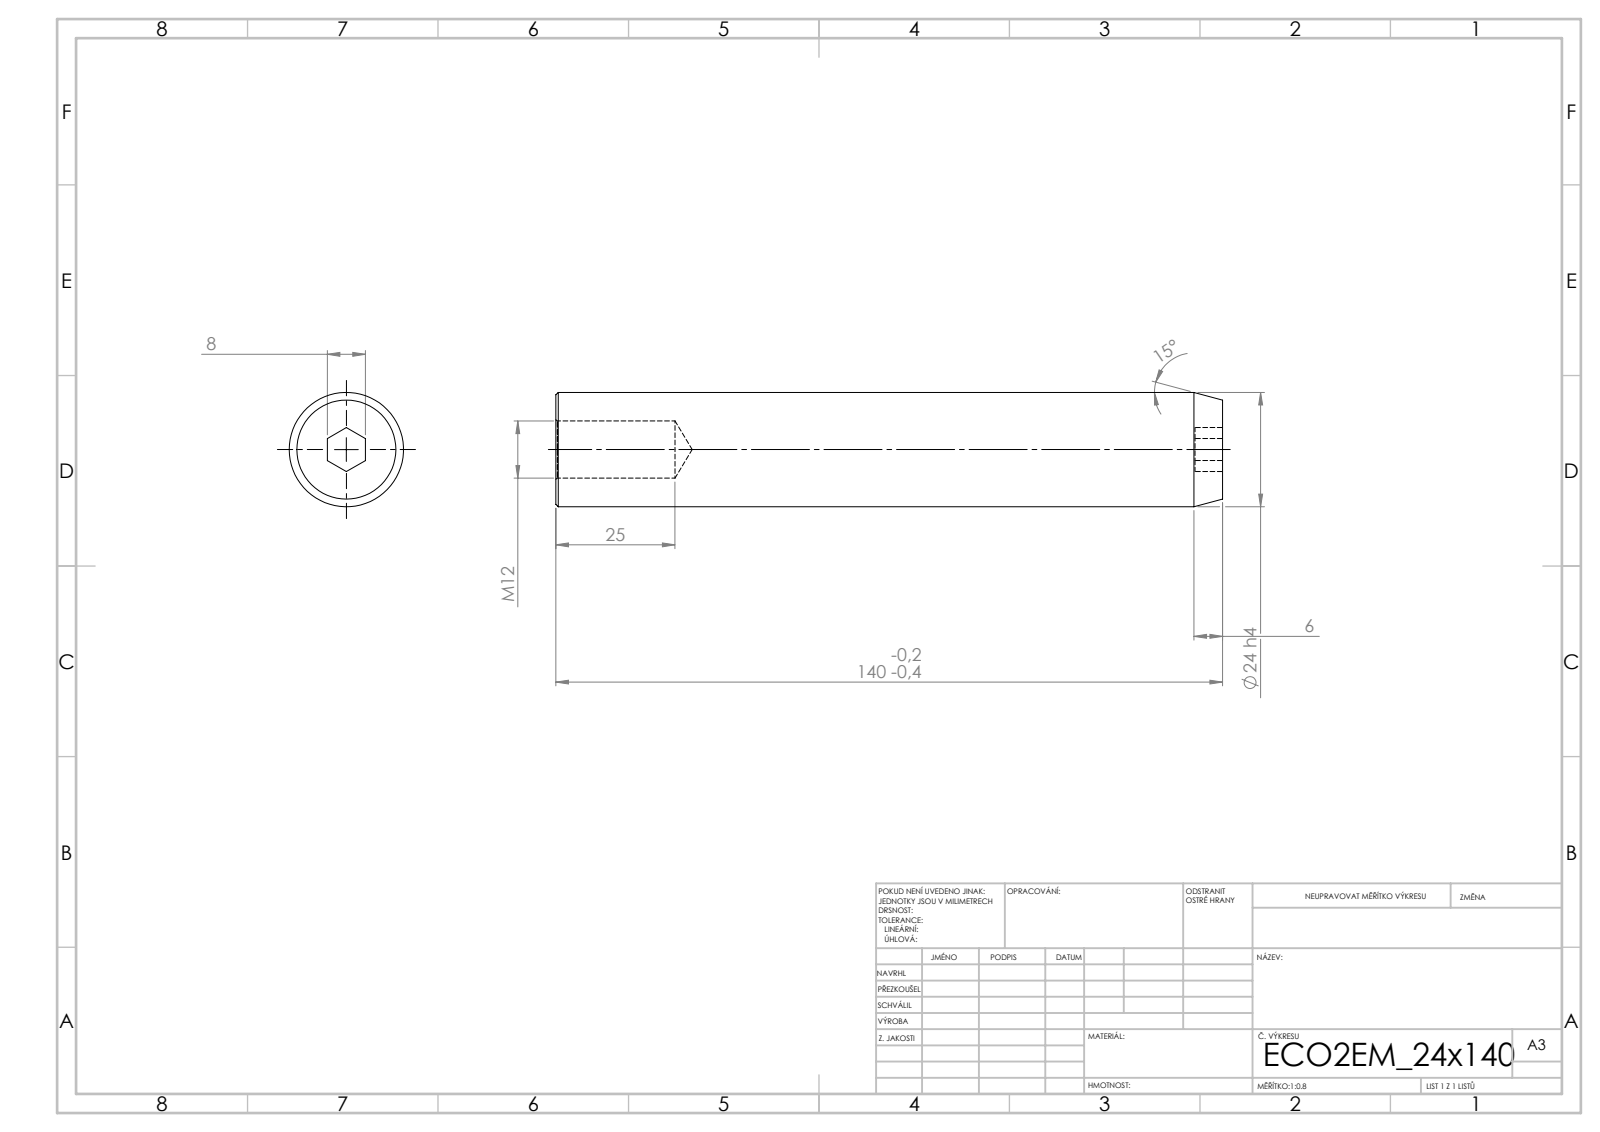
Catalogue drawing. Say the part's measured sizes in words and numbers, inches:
Its 3-D file was written by "SolidWorks 2019 (CONFIG_CONTROL_DESIGN)". It is 1 solid with 21 faces: 9 planar, 4 cylindrical and 8 other. Overall it measures 5.512 by 0.945 by 0.945 inches. Its volume is 3.643 cubic inches and its surface area 19.26 square inches. Round holes: 1 of diameter 0.472. Round bosses or shafts: 1 of diameter 0.945. The main face-to-face distances are 5.512, 0.315, 0.228, 5.283.
